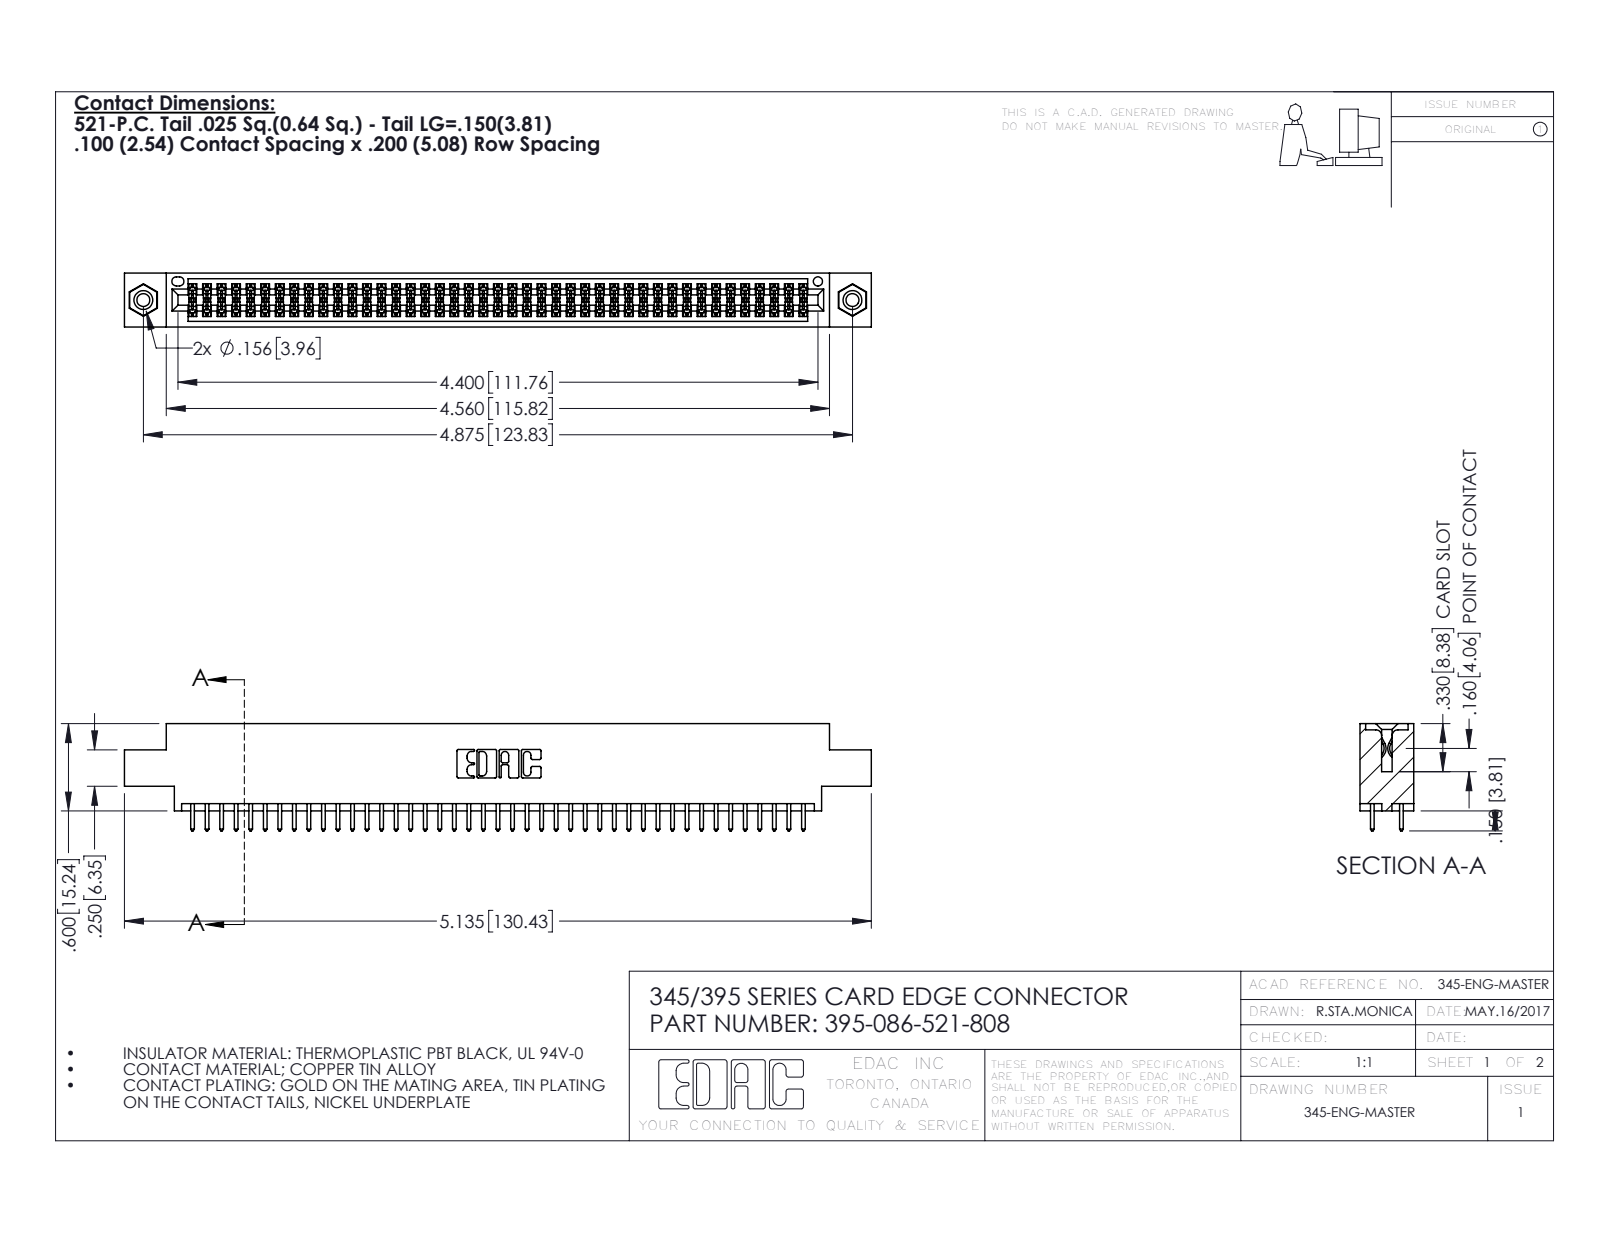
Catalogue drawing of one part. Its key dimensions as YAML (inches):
part_name: "345 Part_0.170 Offset - 0.156 Dia-TI; 345-292-001_345-293-121; 345-250-001_345-250-003-102; 395-086-521-808"
step_written_by: "SolidWorks 2016 (CONFIG_CONTROL_DESIGN)"
units: inches
bodies: {solids: 89, faces: 4490, planar: 2954, cylindrical: 1520, other: 16}
overall_size: [5.135, 0.737, 0.37]
volume: 0.764
surface_area: 28.61
round_holes:
  - {diameter: 0.089, count: 2}
  - {diameter: 0.125, count: 2}
  - {diameter: 0.156, count: 2}
  - {diameter: 0.064, count: 1}
round_bosses_or_shafts:
  - {diameter: 0.155, count: 2}
partial_cylinders:
  - {radius: 0.006, count: 129}
  - {radius: 0.01, count: 86}
  - {radius: 0.01, count: 22}
  - {radius: 0.007, count: 6}
  - {radius: 0.031, count: 6}
  - {radius: 0.026, count: 3}
  - {radius: 0.014, count: 2}
  - {radius: 0.019, count: 2}
face_to_face_distances: [0.072, 0.298, 0.37, 0.2, 0.098, 0.272, 0.025, 0.225, 0.175, 0.149]
hole_center_spacings: [0.27, 4.639, 4.875]
